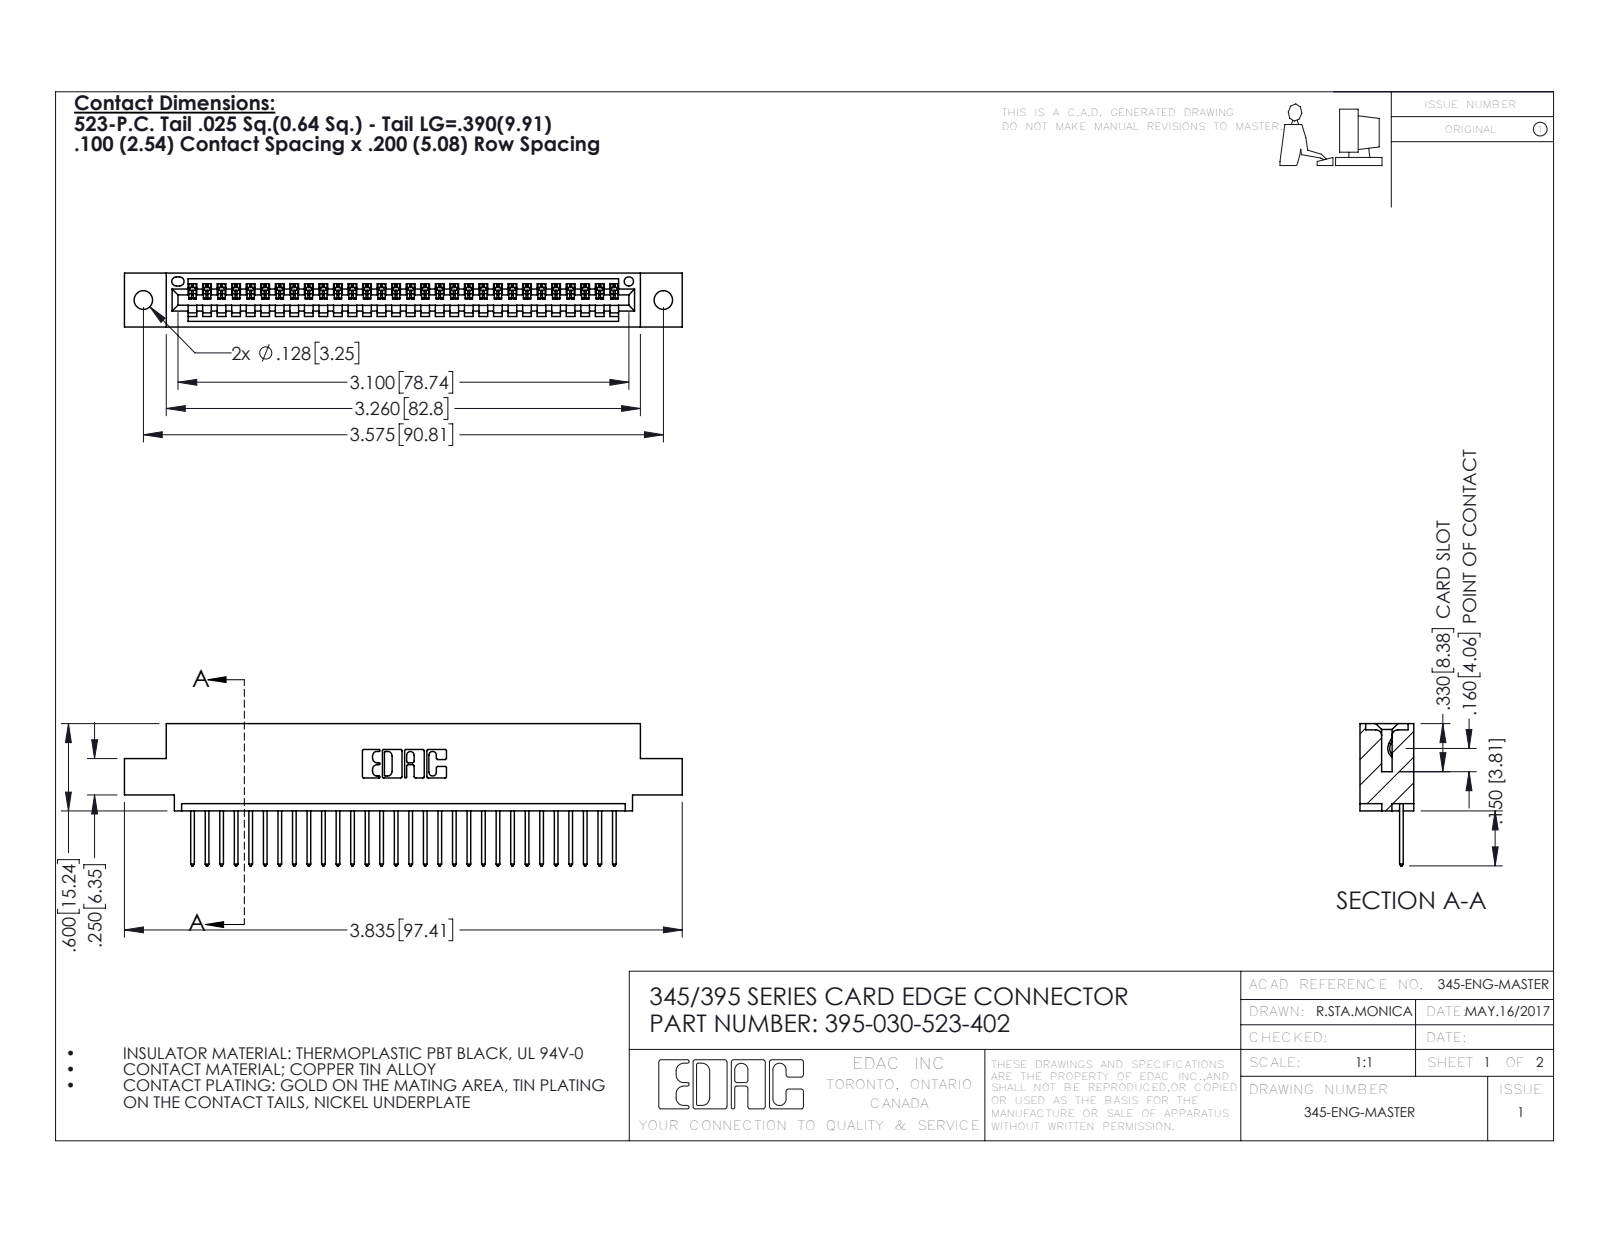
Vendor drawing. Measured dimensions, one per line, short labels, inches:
name: 395-030-523-402; 345-292-001_345-293-123; 345 Part_0.110 Offset - 0.128 Dia
written by: SolidWorks 2016 (CONFIG_CONTROL_DESIGN)
unit: in
bodies: 31 solids, 1870 faces (1284 planar, 586 cylindrical, 0 other)
size: 3.835 × 0.977 × 0.37
volume: 0.551 in³; area: 18.11 in²
holes: 2× ⌀0.128, 1× ⌀0.064
rounds: 60× R0.006, 60× R0.01, 22× R0.01, 6× R0.007, 6× R0.031, 3× R0.026, 2× R0.031, 2× R0.04
face distances: 0.298, 0.072, 0.37, 0.2, 0.098, 0.272, 0.025, 0.225, 0.149, 0.072
hole spacings: 0.27, 3.34, 3.575
